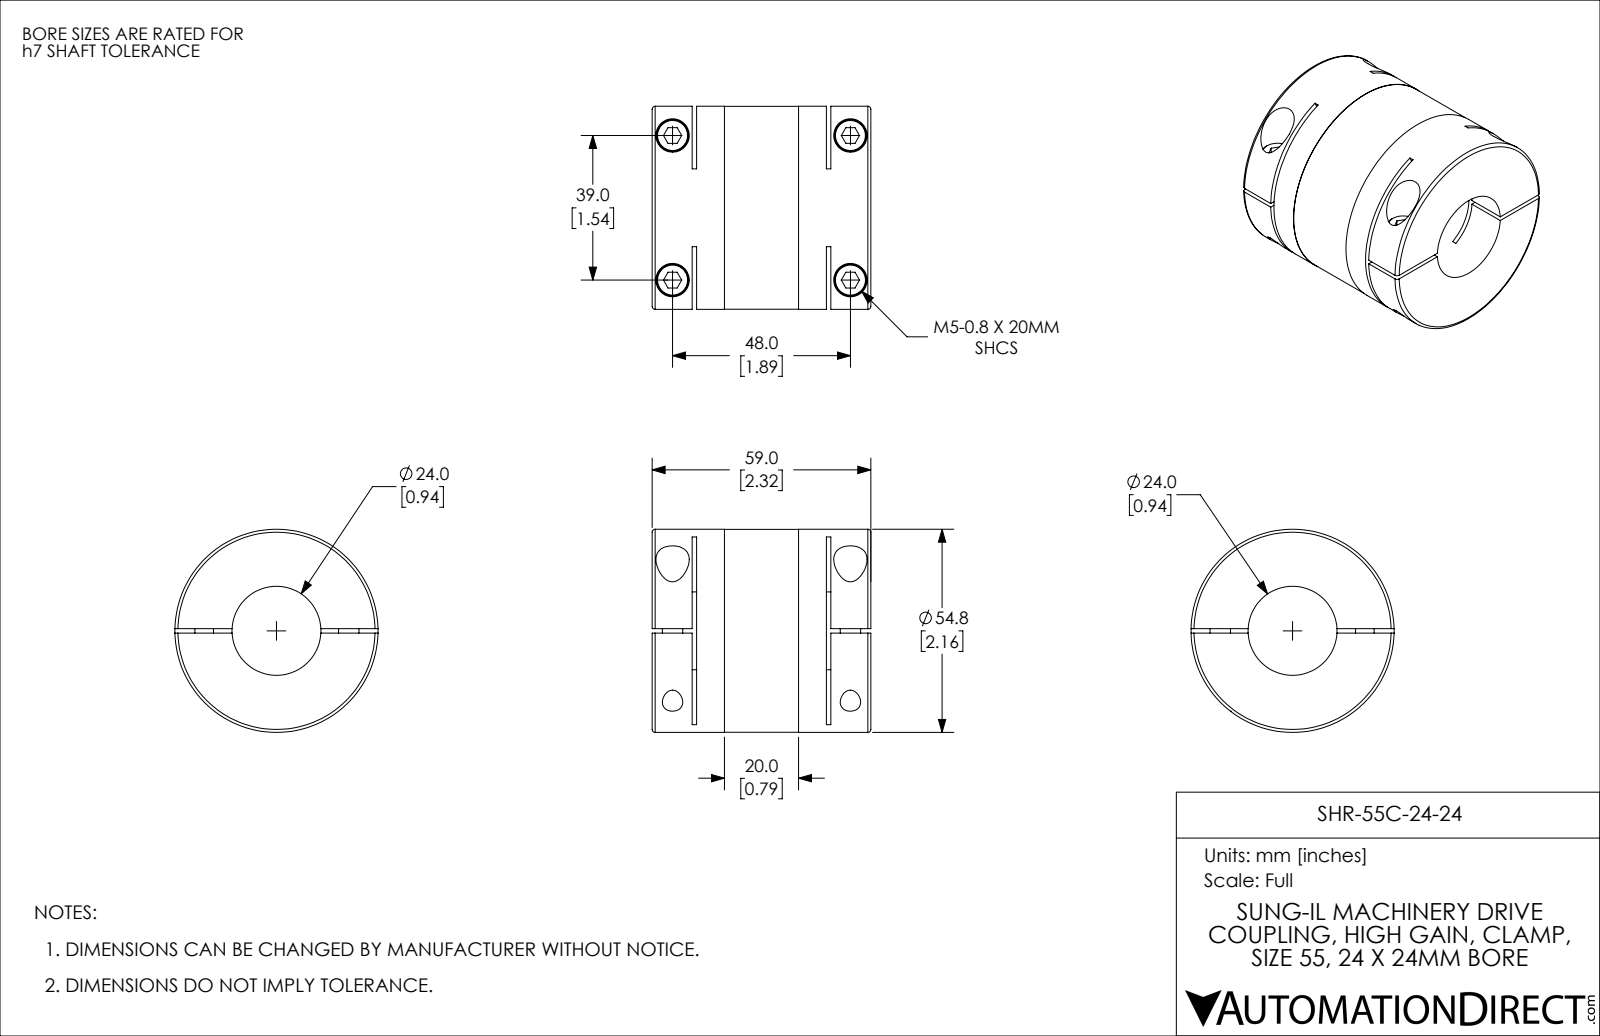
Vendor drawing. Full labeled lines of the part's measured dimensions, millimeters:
Part name (STEP PRODUCT): SHR-55C-24-24
STEP written by: SolidWorks 2021 (CONFIG_CONTROL_DESIGN)
Units: millimetres
Bodies: 1 solid, 144 faces (70 planar, 58 cylindrical, 16 other)
Overall size (bounding box): 59 × 54.8 × 54.8
Volume: 103 792 mm³ · Surface area: 28 398 mm²
Round holes (diameter × count): ⌀5.5 ×4, ⌀9 ×4, ⌀24 ×1, ⌀26 ×1
Round bosses / shafts (diameter × count): ⌀8.5 ×4, ⌀5 ×2, ⌀54.8 ×1, ⌀54.7 ×1
Partial cylindrical surfaces — rounded edges, fillets, slot ends (radius × count): R60 ×2
Main face-to-face distances: 1.2, 12, 47, 10.8, 48.2, 36.2, 59, 35, 37.4, 19.5
Hole centre spacings: 39, 48, 61.85
